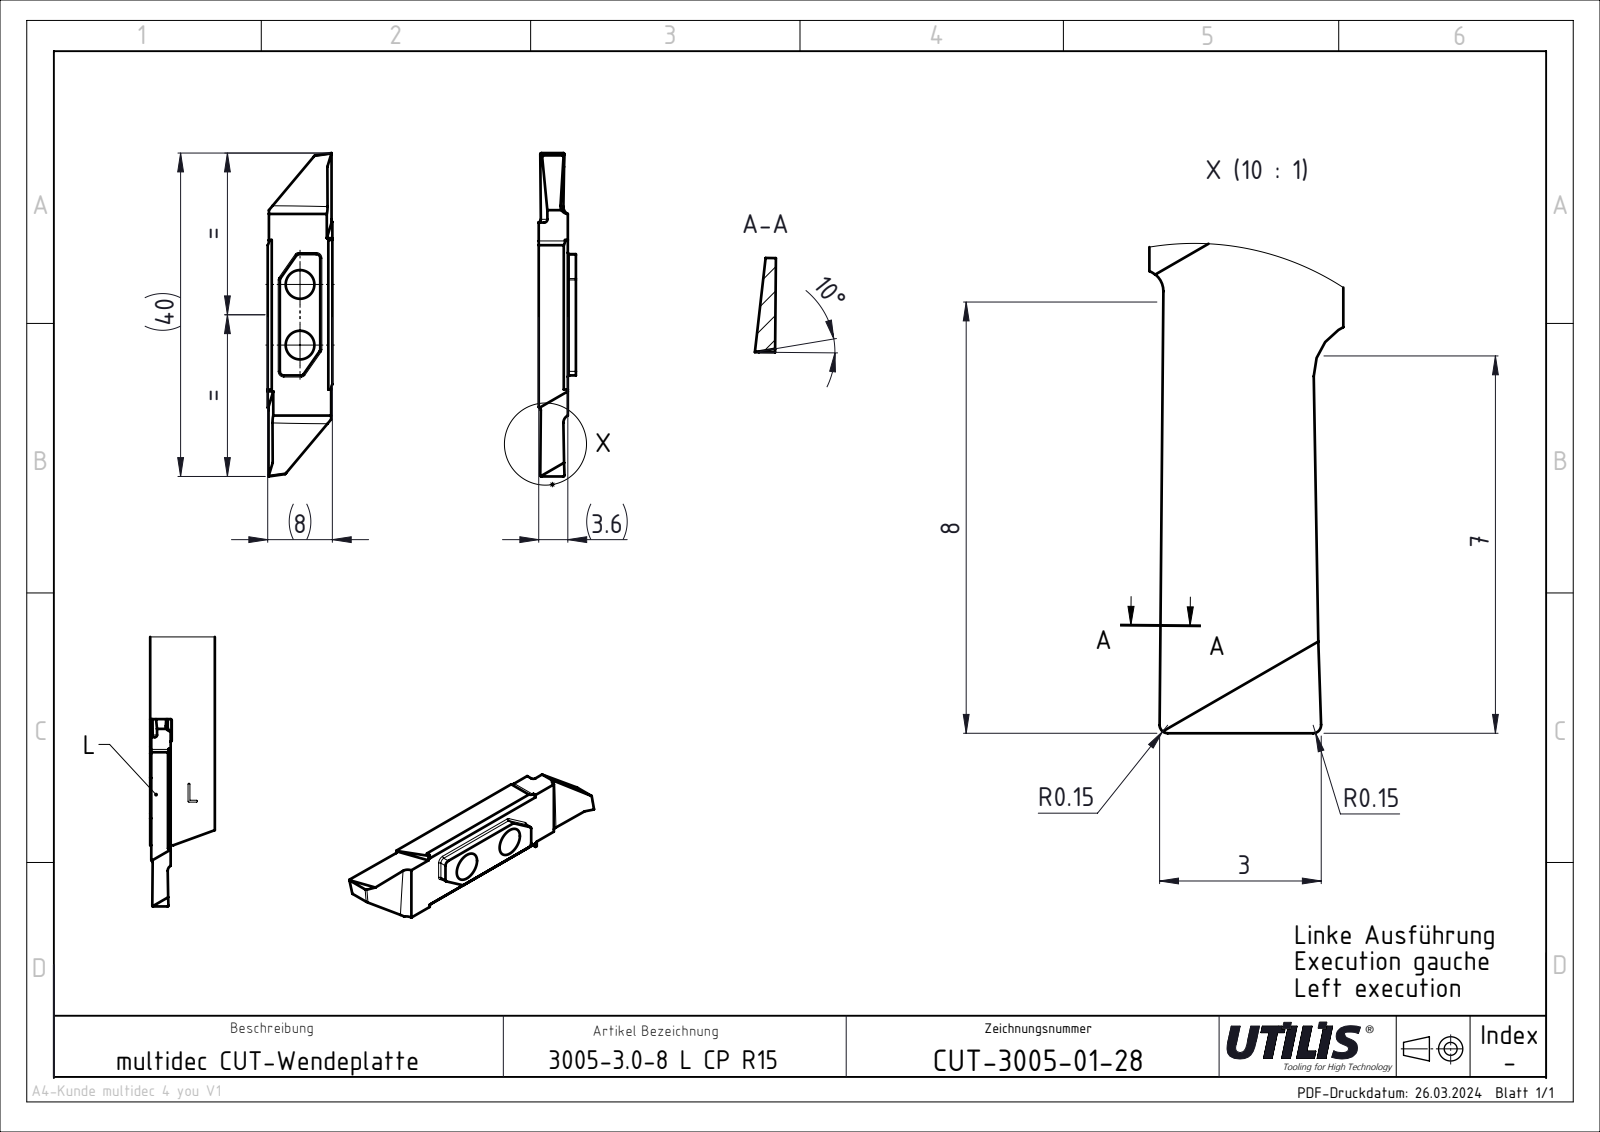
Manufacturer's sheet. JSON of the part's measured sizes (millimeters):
{"part_name": "CUT-3005 CP; ASME Y14.5", "step_written_by": "SolidWorks 2023 SP4 || FormatWorks Professional (AP242_MANAGED_MODEL_BASED_3D_ENGINEERING_MIM_LF)", "units": "millimeters", "bodies": {"solids": 1, "faces": 34, "planar": 20, "cylindrical": 14, "other": 0}, "overall_size": [40, 8, 3.6], "volume_mm3": 857, "surface_area_mm2": 875, "round_holes": [[3.55, 2]], "partial_cylinders_radius": [[0.15, 4], [1, 4], [0.4, 2]], "face_to_face_distances": [3.6, 8, 22.54, 7.85, 7.7, 40, 10.75, 29.25, 18.5], "hole_center_spacings": [7.49]}
